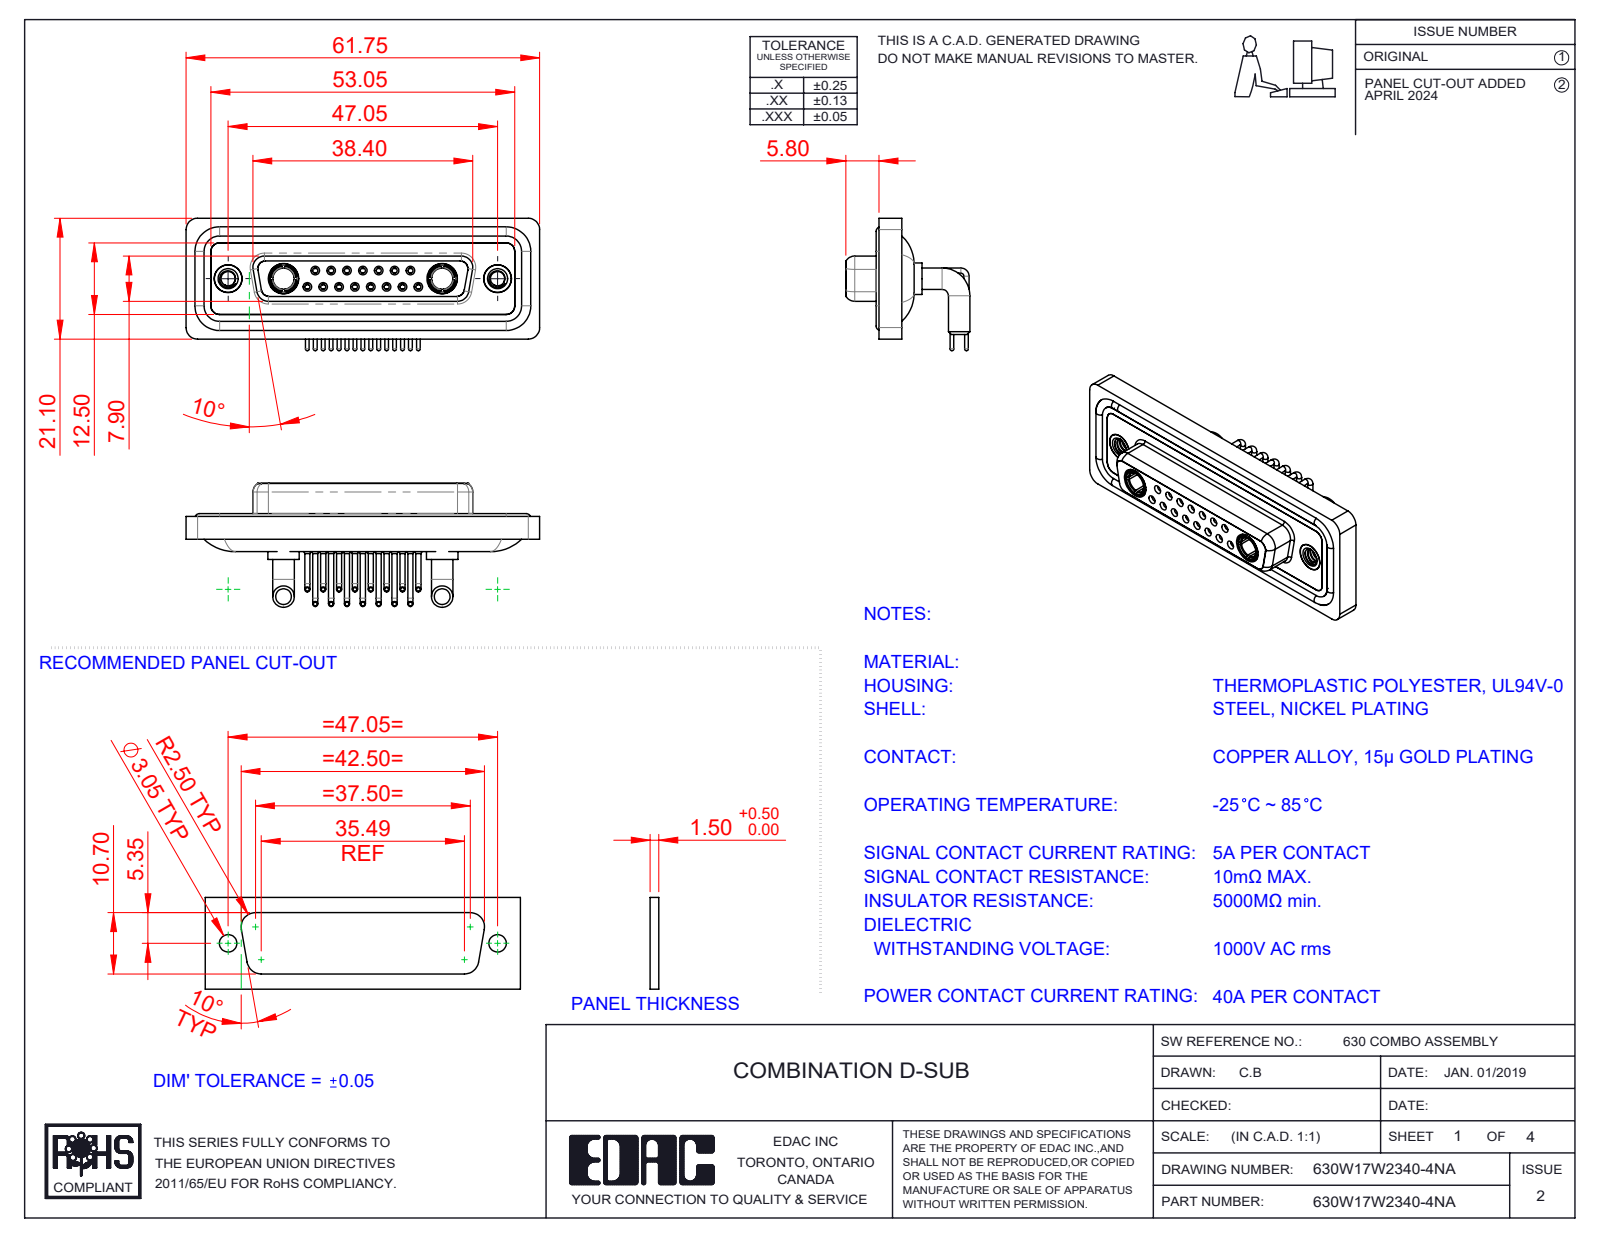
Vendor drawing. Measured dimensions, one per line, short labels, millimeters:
name: 630Combo Housing_17W2; 630Combo Shell Rear_25 Contacts; Power Socket_40A RA; 630Combo Threaded Rivet_A (+5 more)
written by: SolidWorks 2023 (CONFIG_CONTROL_DESIGN)
unit: mm
bodies: 26 solids, 1331 faces (388 planar, 581 cylindrical, 362 other)
size: 61.75 × 23.12 × 21.68
volume: 8 625 mm³; area: 14 621 mm²
holes: 15× ⌀0.9, 15× ⌀1.1, 15× ⌀1.5, 15× ⌀2, 8× ⌀1.6, 7× ⌀1.7, 4× ⌀4.85, 2× ⌀2.5, 2× ⌀3.7, 2× ⌀4, 2× ⌀4.05, 2× ⌀5
bosses: 15× ⌀0.9, 15× ⌀0.65, 11× ⌀1.6, 4× ⌀3.75, 2× ⌀5.5, 2× ⌀5.2, 2× ⌀4.96, 2× ⌀4.95
rounds: 18× R1.5, 18× R2, 8× R1.35, 8× R1.6, 4× R0.25, 4× R0.5, 4× R0.6, 4× R0.65
face distances: 0.4, 1.8, 4.1, 1.1, 1.6, 3.1, 2.5, 1.5, 3.7, 1.4
hole spacings: 3.16, 2.77, 5.54, 8.31, 5.04, 7.49, 11.08, 5.03
